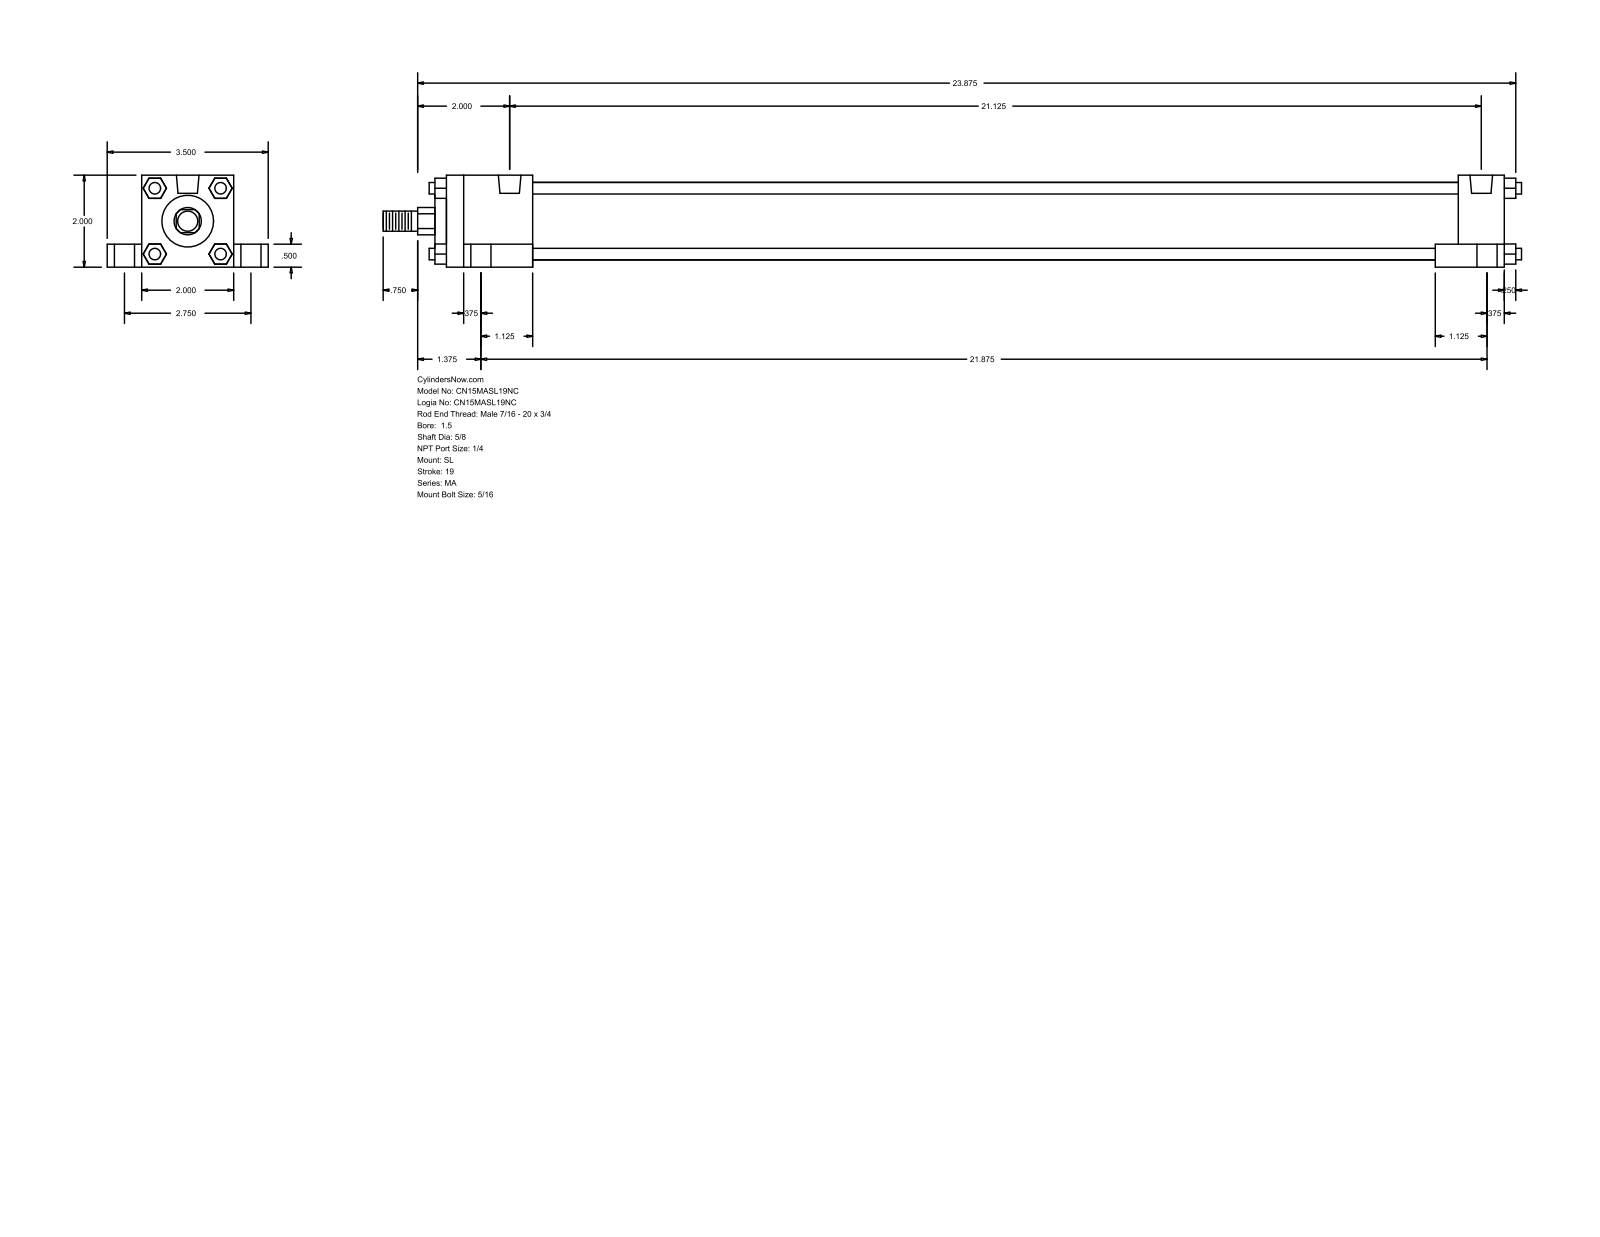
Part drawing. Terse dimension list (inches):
name: MA_SL__0150_0.625
written by: GSSL Pune (CONFIG_CONTROL_DESIGN)
unit: in
bodies: 0 solids, 148 faces (112 planar, 36 cylindrical, 0 other)
size: 24.75 × 3.5 × 2
holes: 4× ⌀0.313, 4× ⌀0.437, 4× ⌀0.687, 2× ⌀0.492
bosses: 4× ⌀0.25, 1× ⌀1.69, 1× ⌀1.125, 1× ⌀0.625, 1× ⌀0.437
rounds: 1× R0.297
face distances: 2, 0.75, 1.5, 23, 2.75, 0.5, 20.125, 0.375, 22, 1
hole spacings: 1.38, 1.51, 2.75, 21.125, 21.294, 21.794, 21.875, 22.047
